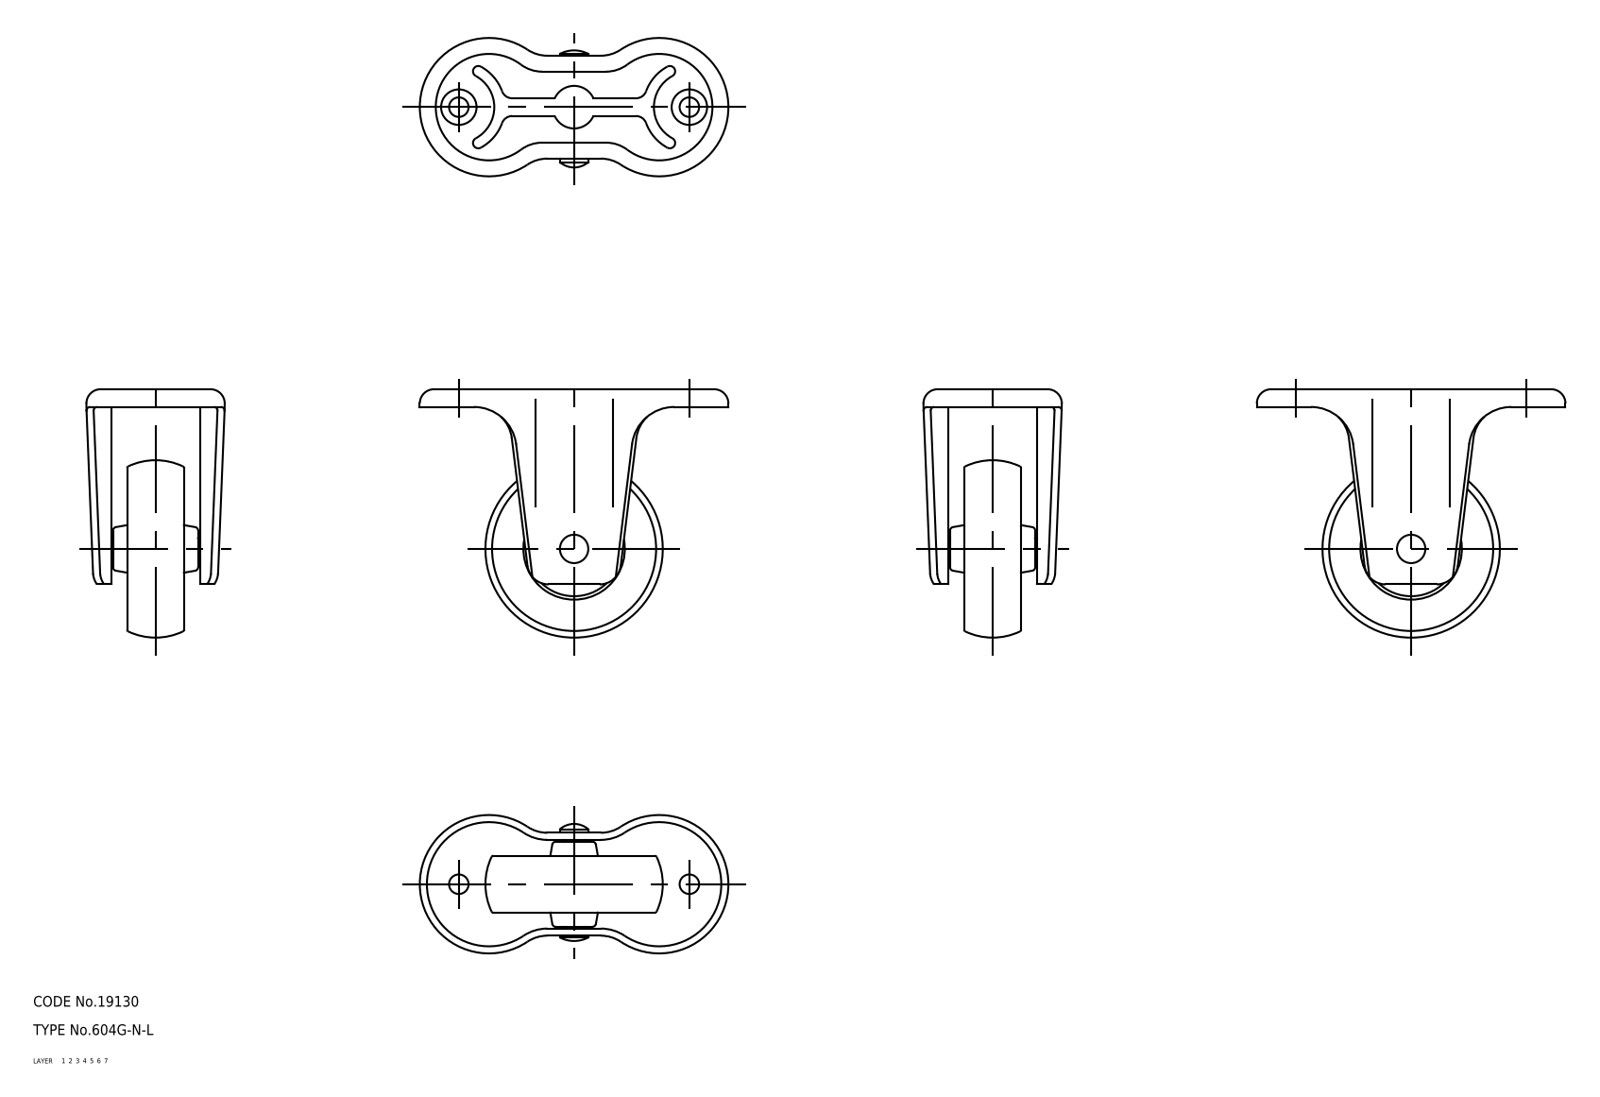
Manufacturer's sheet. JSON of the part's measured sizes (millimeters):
{"part_name": "wheel; axle; No_604G_N_L_14427_36", "step_written_by": "CADfix (AUTOMOTIVE_DESIGN)", "units": "millimeters", "bodies": {"solids": 3, "faces": 168, "planar": 0, "cylindrical": 0, "other": 168}, "overall_size": [87, 70, 39], "volume_mm3": 39556, "surface_area_mm2": 22290}
